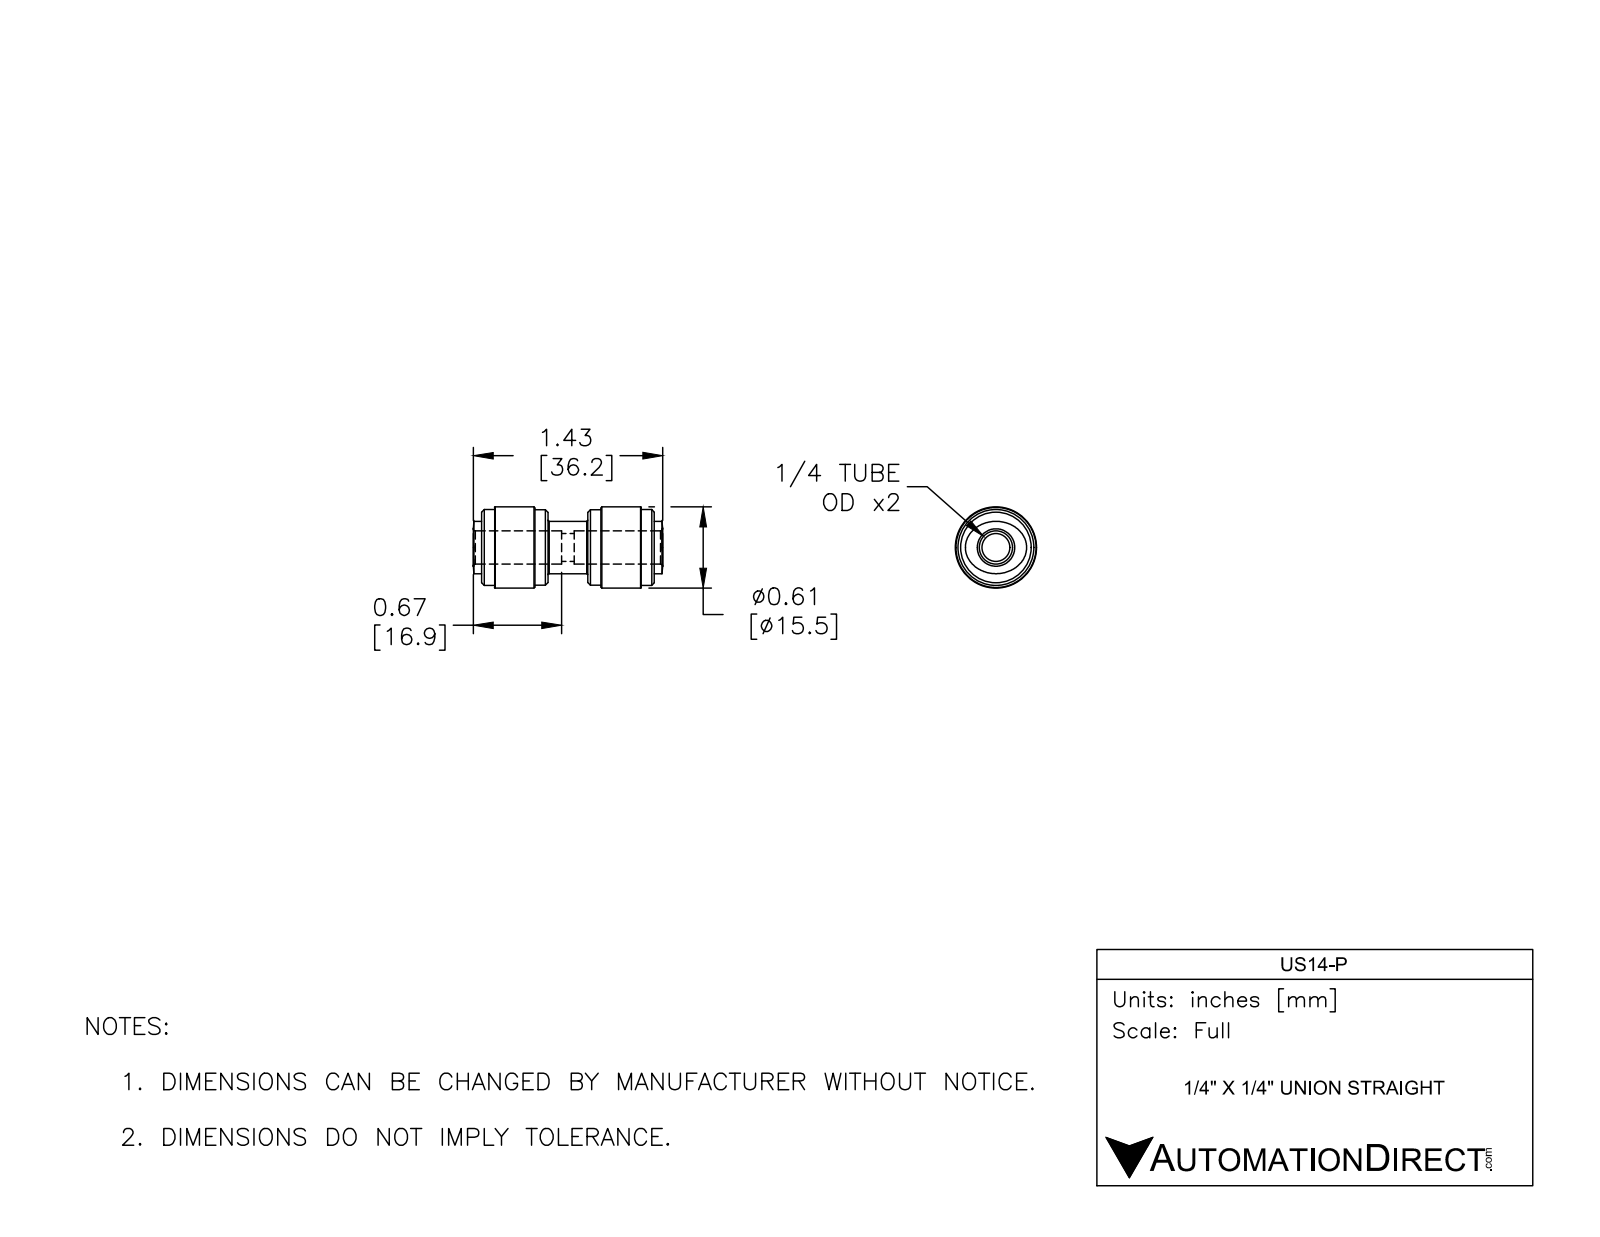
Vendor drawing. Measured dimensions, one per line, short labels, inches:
name: US14-P
written by: SolidWorks 2017 (AUTOMOTIVE_DESIGN)
unit: in
bodies: 1 solid, 62 faces (10 planar, 20 cylindrical, 32 other)
size: 1.425 × 0.61 × 0.61
volume: 0.261 in³; area: 4.23 in²
holes: 1× ⌀0.209, 1× ⌀0.25
bosses: 1× ⌀0.61, 1× ⌀0.571, 1× ⌀0.567, 1× ⌀0.394
face distances: 0.799, 0.5, 0.098, 0.402, 0.299, 1.299, 1.201, 0.701, 0.898, 0.303
